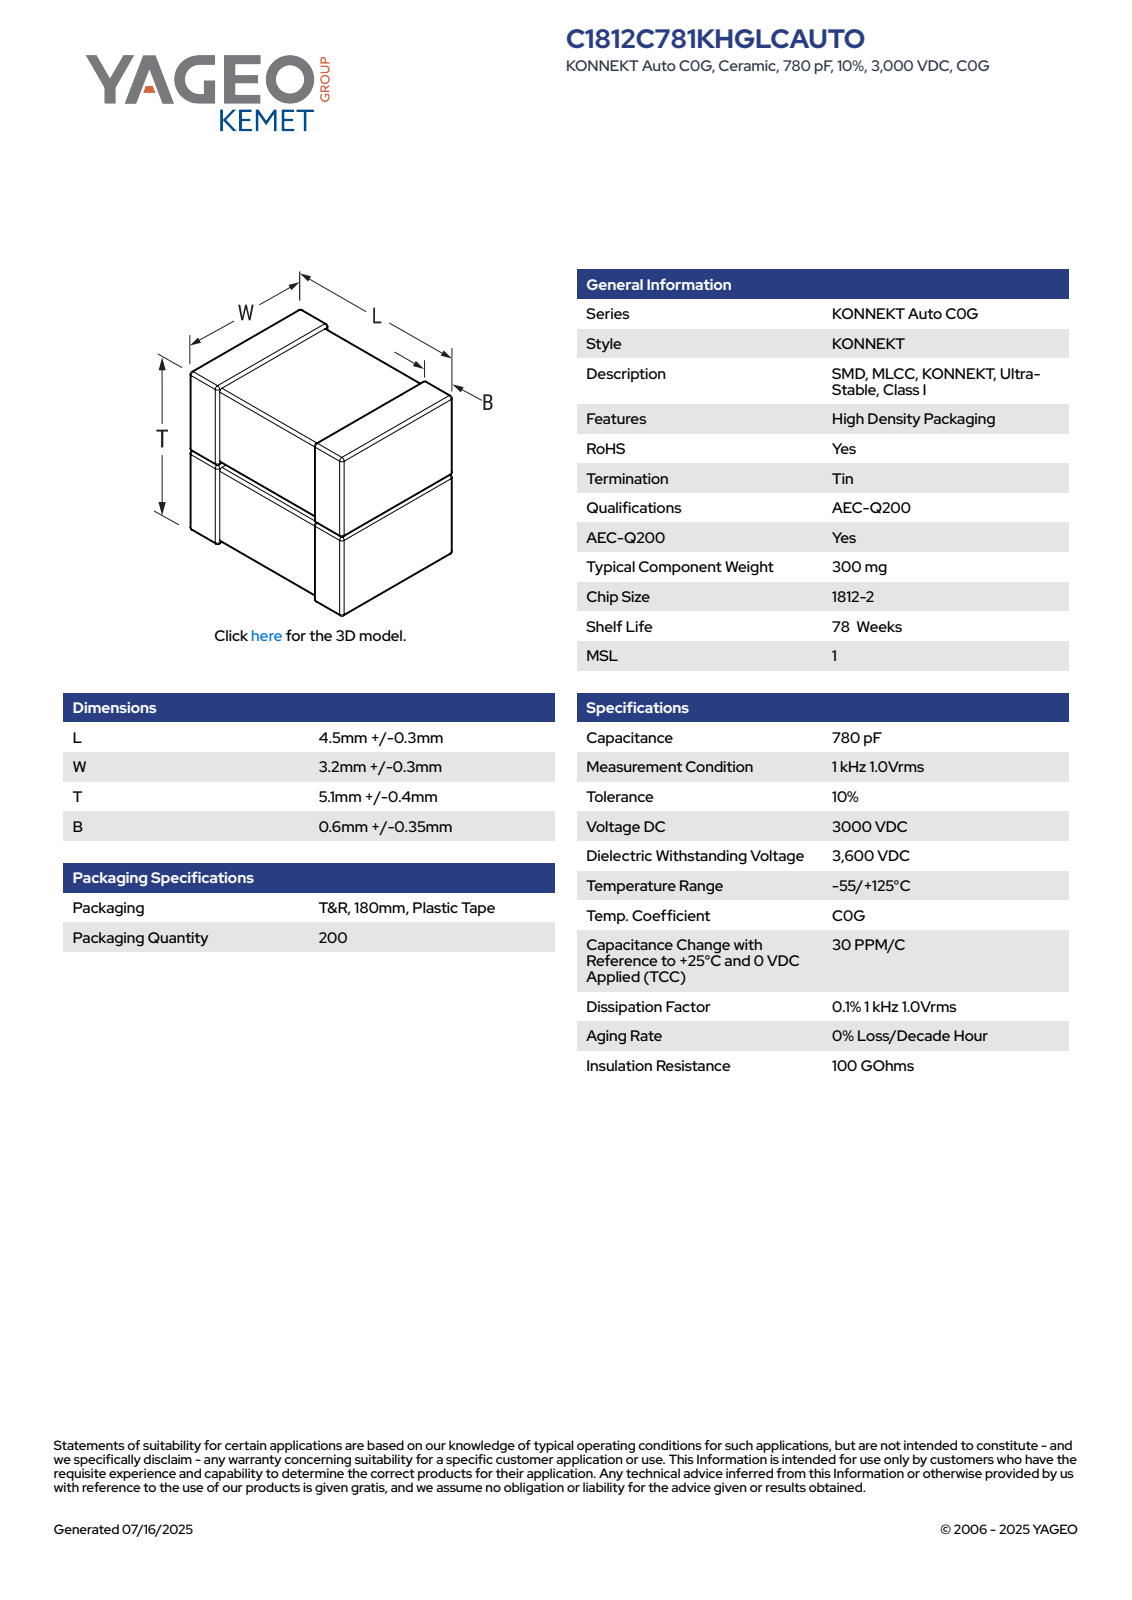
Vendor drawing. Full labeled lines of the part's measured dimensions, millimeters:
Part name (STEP PRODUCT): CCSS_K2T_1812-2_L4.8W3.5B0.95T5.5
STEP written by: SolidWorks 2020 (AUTOMOTIVE_DESIGN)
Units: millimetres
Bodies: 4 solids, 189 faces (81 planar, 76 cylindrical, 32 other)
Overall size (bounding box): 5.5 × 4.8 × 3.5
Volume: 87 mm³ · Surface area: 145 mm²
Main face-to-face distances: 2.61, 2.75, 4.8, 3.43, 3.36, 2.68, 2.82, 5.43, 5.36, 3.5
